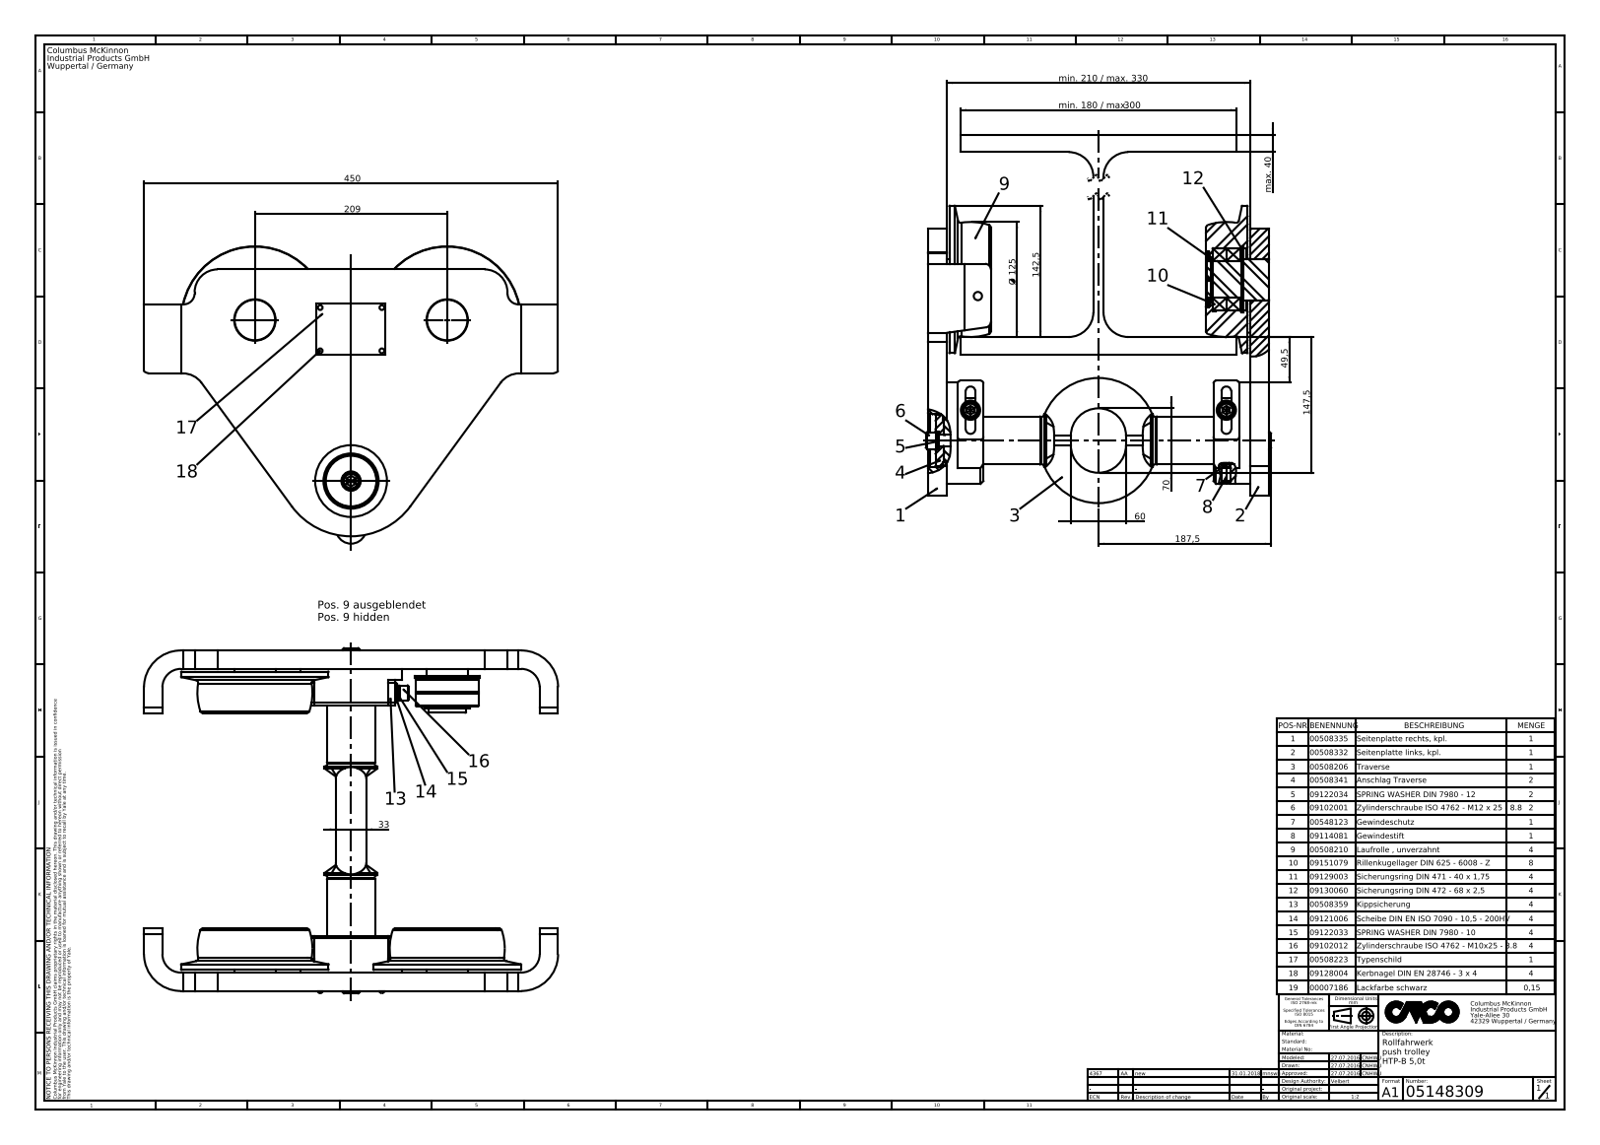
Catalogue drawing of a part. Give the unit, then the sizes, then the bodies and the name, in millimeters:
Units: millimetres
Overall size (bounding box): 461.5 × 450 × 375
Round holes (diameter × count): ⌀3 ×8, ⌀2.5 ×5, ⌀3.5 ×4, ⌀8.5 ×3, ⌀10.2 ×3, ⌀2 ×2, ⌀9 ×2, ⌀10.5 ×2, ⌀37.5 ×2, ⌀40 ×2, ⌀45 ×2, ⌀55.4 ×2
Round bosses / shafts (diameter × count): ⌀5.2 ×4, ⌀10 ×3, ⌀160 ×2, ⌀71 ×2, ⌀49.49 ×2, ⌀21 ×2, ⌀16 ×2, ⌀110 ×1
Partial cylindrical surfaces — rounded edges, fillets, slot ends (radius × count): R3 ×12, R2.5 ×5, R5.25 ×4, R6 ×4, R20 ×4, R25 ×4, R27 ×4, R40 ×4
Main face-to-face distances: 19, 281, 159.5, 20, 179.5, 190.5, 350, 170.5, 300, 11
Hole centre spacings: 9.87, 12.01, 31.59, 145.41, 209, 21.74, 6.25, 7.5
Volume: 13 080 000 mm³ · Surface area: 1 738 000 mm²
Bodies: 59 solids, 1200 faces (402 planar, 462 cylindrical, 336 other)
Part name (STEP PRODUCT): HTP-B 5,0t
STEP written by: SolidWorks 2015 (AUTOMOTIVE_DESIGN)
